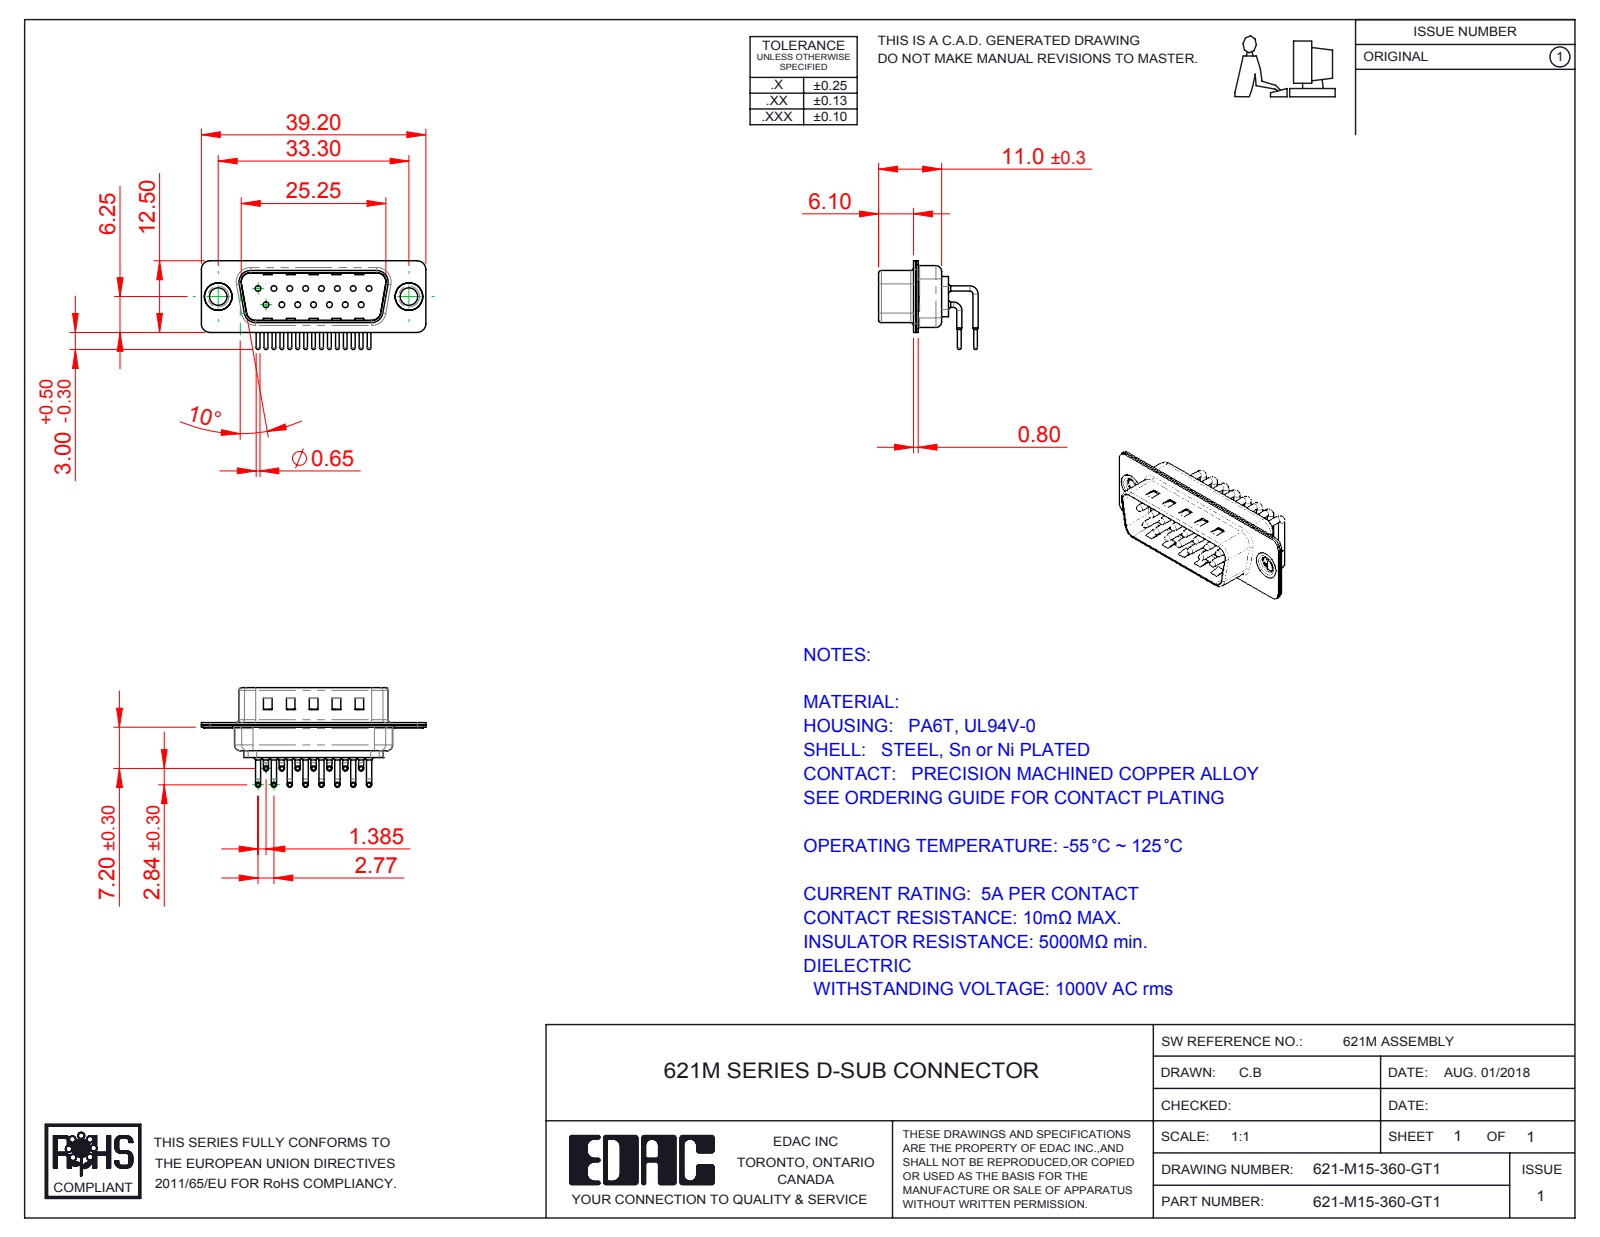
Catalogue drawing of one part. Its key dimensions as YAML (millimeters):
part_name: "621-M15-360-GT1; 621M Thru Hole Rivet; 621M Contact Row 2; 621M Housing_15 Contacts (+3 more)"
step_written_by: "SolidWorks 2016 (CONFIG_CONTROL_DESIGN)"
units: millimeters
bodies: {solids: 20, faces: 1964, planar: 1099, cylindrical: 657, other: 208}
overall_size: [39.2, 17.39, 15.49]
volume: 1859
surface_area: 5111
round_holes:
  - {diameter: 1, count: 15}
  - {diameter: 1.7, count: 15}
  - {diameter: 2, count: 15}
  - {diameter: 3.05, count: 2}
  - {diameter: 4, count: 2}
  - {diameter: 4.8, count: 2}
round_bosses_or_shafts:
  - {diameter: 0.9, count: 30}
  - {diameter: 1.5, count: 15}
  - {diameter: 0.65, count: 15}
  - {diameter: 5, count: 2}
  - {diameter: 4.9, count: 2}
  - {diameter: 3.55, count: 2}
partial_cylinders:
  - {radius: 1.5, count: 16}
  - {radius: 1.01, count: 15}
  - {radius: 2, count: 12}
  - {radius: 0.5, count: 8}
  - {radius: 1.6, count: 8}
  - {radius: 0.25, count: 4}
  - {radius: 0.6, count: 4}
  - {radius: 0.65, count: 4}
face_to_face_distances: [0.4, 0.85, 9.55, 8.7, 1.25, 0.8, 10.4, 1.5, 0.35, 1.9]
hole_center_spacings: [3.16, 2.77, 5.54, 8.31, 11.08, 5.03, 5.04, 7.48]
